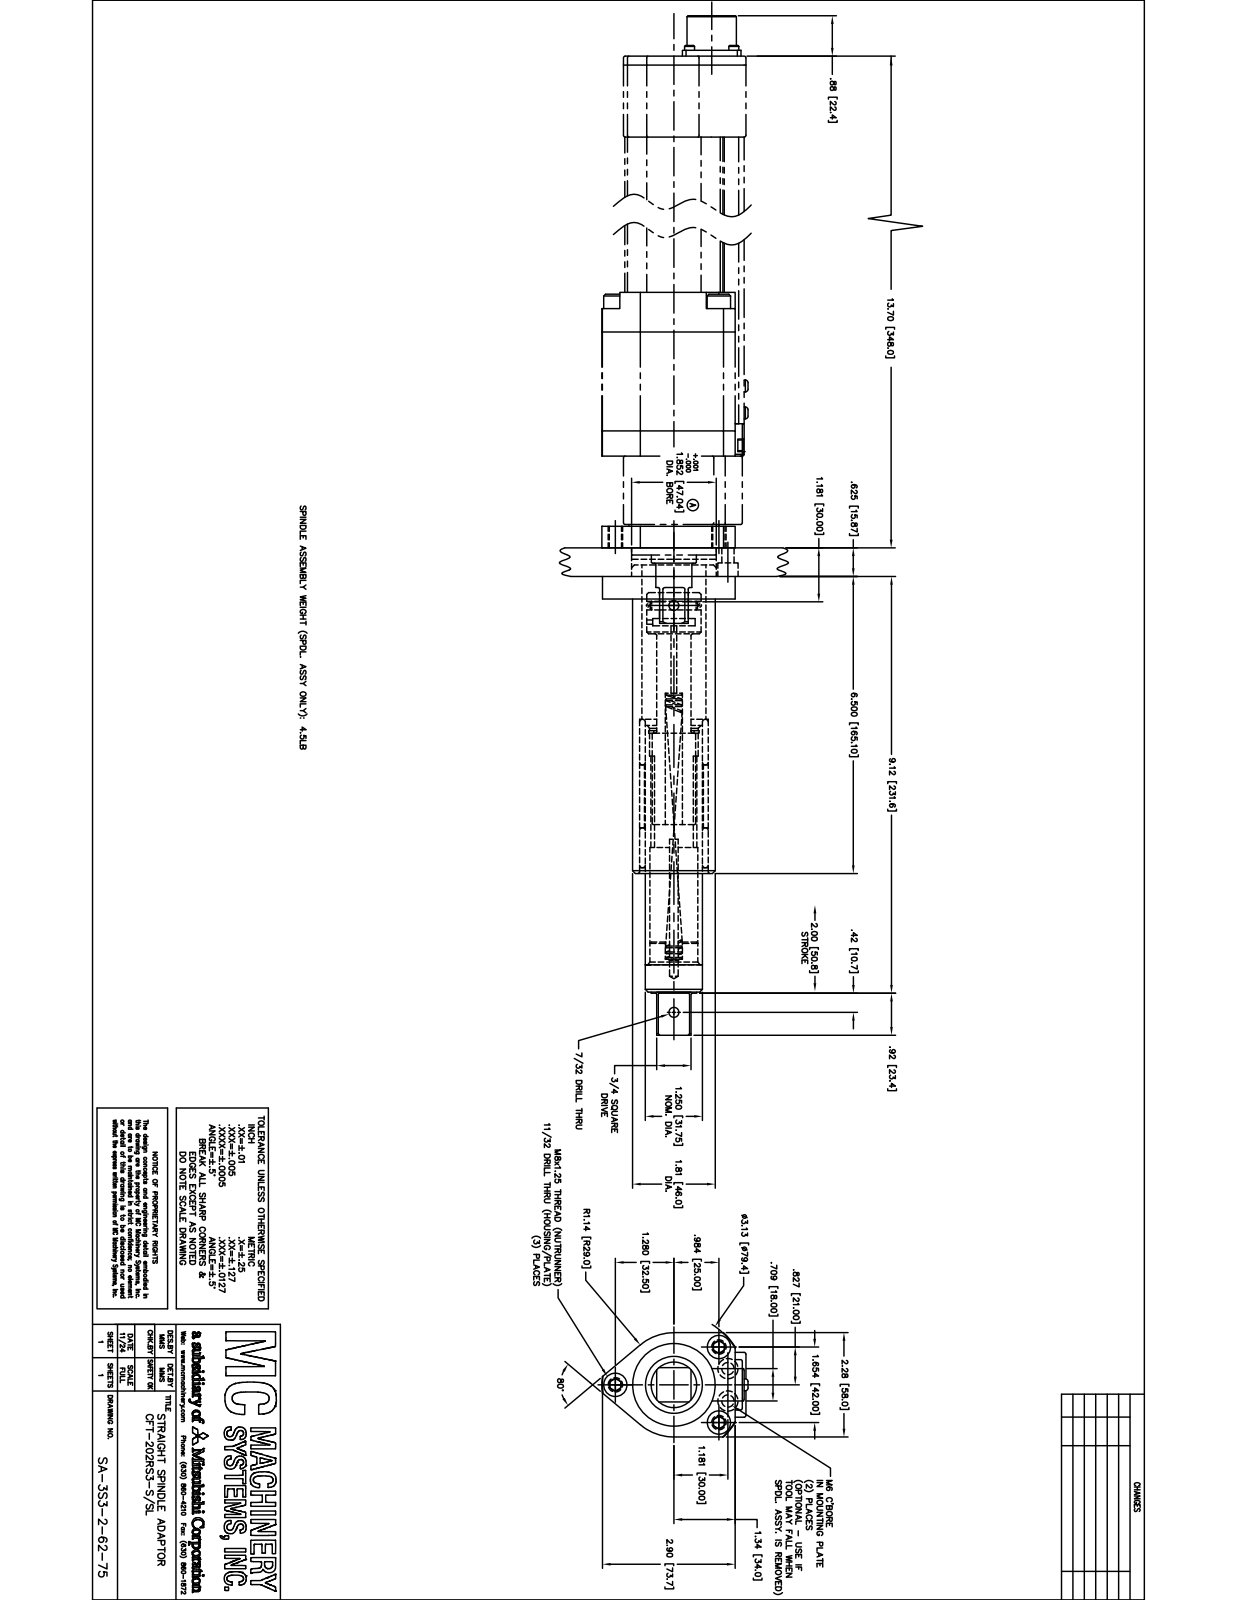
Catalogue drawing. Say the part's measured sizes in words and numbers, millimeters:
The part is named "SA-3S3-2-62-75". Its 3-D file was written by "SolidWorks 2024 (CONFIG_CONTROL_DESIGN)". It is 9 solids with 179 faces: 52 planar, 83 cylindrical and 44 other. Overall it measures 261.6 by 73.7 by 57.9 millimeters. Its volume is 264 500 cubic millimeters and its surface area 123 400 square millimeters. Round holes: 3 of diameter 8.7, 1 of diameter 3.2, 1 of diameter 4.7, 1 of diameter 5.5, 1 of diameter 5.6, 1 of diameter 9.4, 1 of diameter 9.7, 1 of diameter 23.6, 1 of diameter 25.5, 1 of diameter 26.6, 1 of diameter 27, 1 of diameter 28.7. Round bosses or shafts: 1 of diameter 47, 1 of diameter 38.1, 1 of diameter 37.9, 1 of diameter 32.4, 1 of diameter 30.1, 1 of diameter 24.6, 1 of diameter 24.1, 1 of diameter 23.8. Partial cylindrical surfaces (rounded edges, fillets, slot ends): 4 of radius 0.8, 2 of radius 79.5, 1 of radius 29, 1 of radius 39.7. The main face-to-face distances are 12.7, 203.4, 16, 216.1, 6.2, 18.9, 222.3, 15.9, 33.6, 27.4. The hole center spacings are 32.6, 32.6, 61.2, 32.5, 32.6, 42, 226.4.
